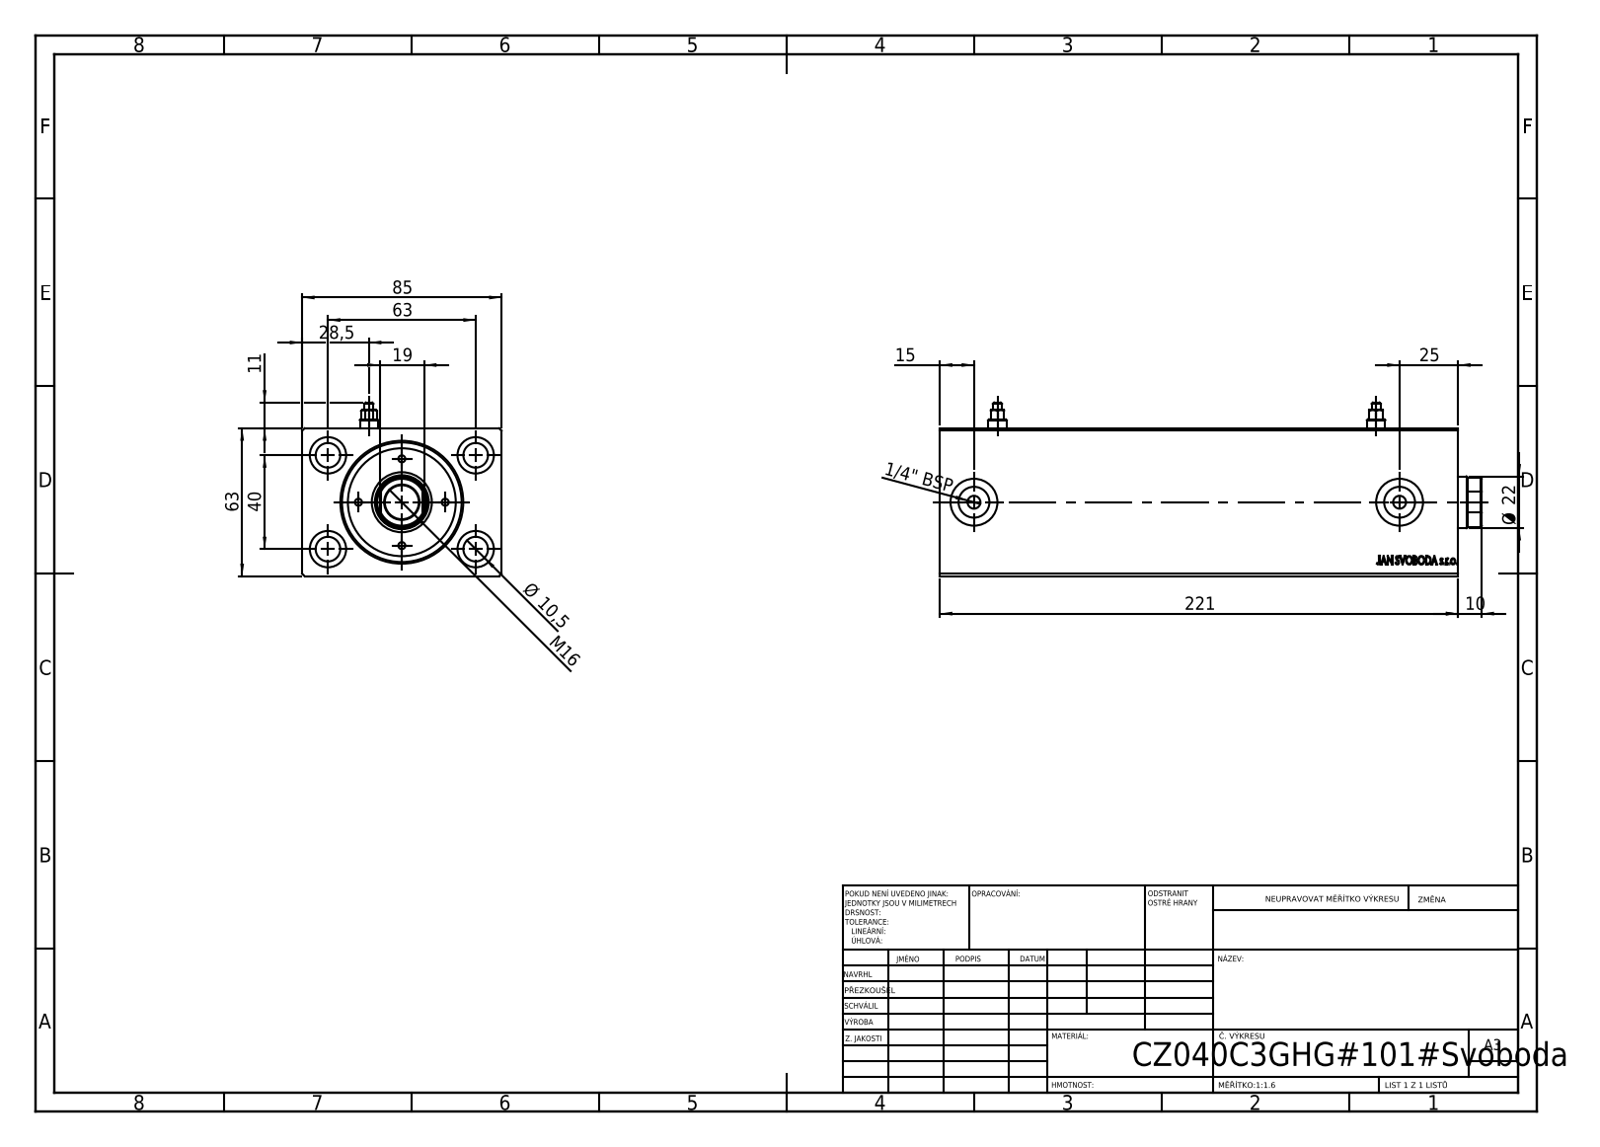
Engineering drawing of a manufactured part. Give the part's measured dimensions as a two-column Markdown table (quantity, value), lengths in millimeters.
| quantity | value |
| --- | --- |
| STEP written by | SolidWorks 2019 (CONFIG_CONTROL_DESIGN) |
| units | millimeters |
| bodies | 1 solid, 825 faces (397 planar, 46 cylindrical, 382 other) |
| overall size | 221 × 85 × 63 |
| volume | 827 254 mm³ |
| surface area | 133 093 mm² |
| round holes (diameter × count) | 10.5 × 4, 15.5 × 4, 5.5 × 2, 8 × 2, 13.16 × 2, 20 × 2, 36 × 1, 40 × 1, 51 × 1 |
| main face-to-face distances | 63, 85, 221, 205.7, 15.3, 220.8, 15.1, 10.33, 210.67, 10 |
| hole center spacings | 37.31, 40, 63, 74.63, 161.5, 181.5 |
